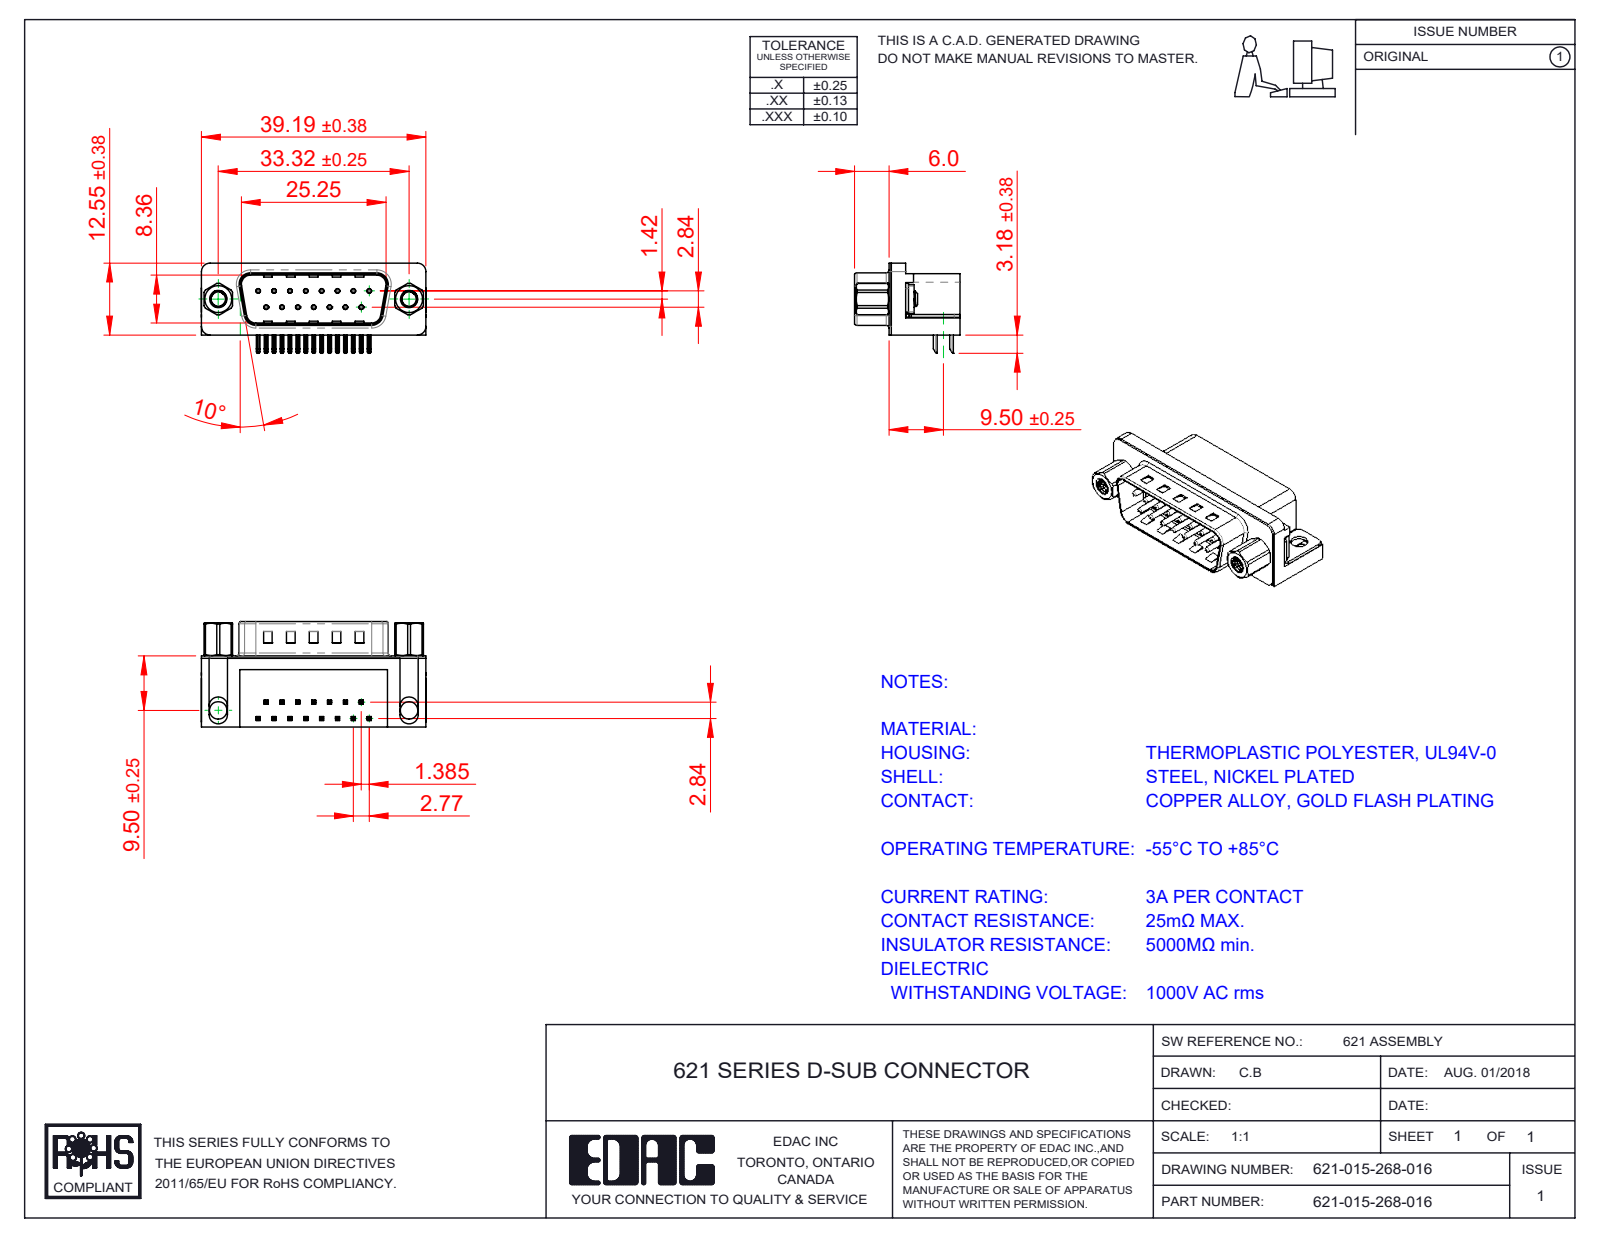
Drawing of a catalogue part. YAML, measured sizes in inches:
part_name: "621 Thru Hole Board Mount; 621 Contact Top; 621 Contact Bottom; 621 Shell_15 Socket (+4 more)"
step_written_by: "SolidWorks 2016 (CONFIG_CONTROL_DESIGN)"
units: inches
bodies: {solids: 23, faces: 1623, planar: 913, cylindrical: 541, other: 169}
overall_size: [1.544, 0.724, 0.619]
volume: 0.284
surface_area: 9.562
round_holes:
  - {diameter: 0.014, count: 15}
  - {diameter: 0.031, count: 15}
  - {diameter: 0.098, count: 2}
  - {diameter: 0.12, count: 2}
  - {diameter: 0.157, count: 2}
  - {diameter: 0.189, count: 2}
  - {diameter: 0.197, count: 2}
round_bosses_or_shafts:
  - {diameter: 0.03, count: 15}
  - {diameter: 0.193, count: 2}
  - {diameter: 0.187, count: 2}
  - {diameter: 0.154, count: 2}
  - {diameter: 0.118, count: 2}
partial_cylinders:
  - {radius: 0.01, count: 68}
  - {radius: 0.005, count: 30}
  - {radius: 0.039, count: 16}
  - {radius: 0.02, count: 9}
  - {radius: 0.063, count: 8}
  - {radius: 0.059, count: 6}
  - {radius: 0.035, count: 4}
  - {radius: 0.079, count: 4}
face_to_face_distances: [0.016, 0.472, 0.407, 0.488, 0.083, 0.412, 0.067, 0.428, 0.345, 0.374]
hole_center_spacings: [0.124, 0.109, 0.218, 0.327, 0.436, 0.198, 0.198, 0.294]
